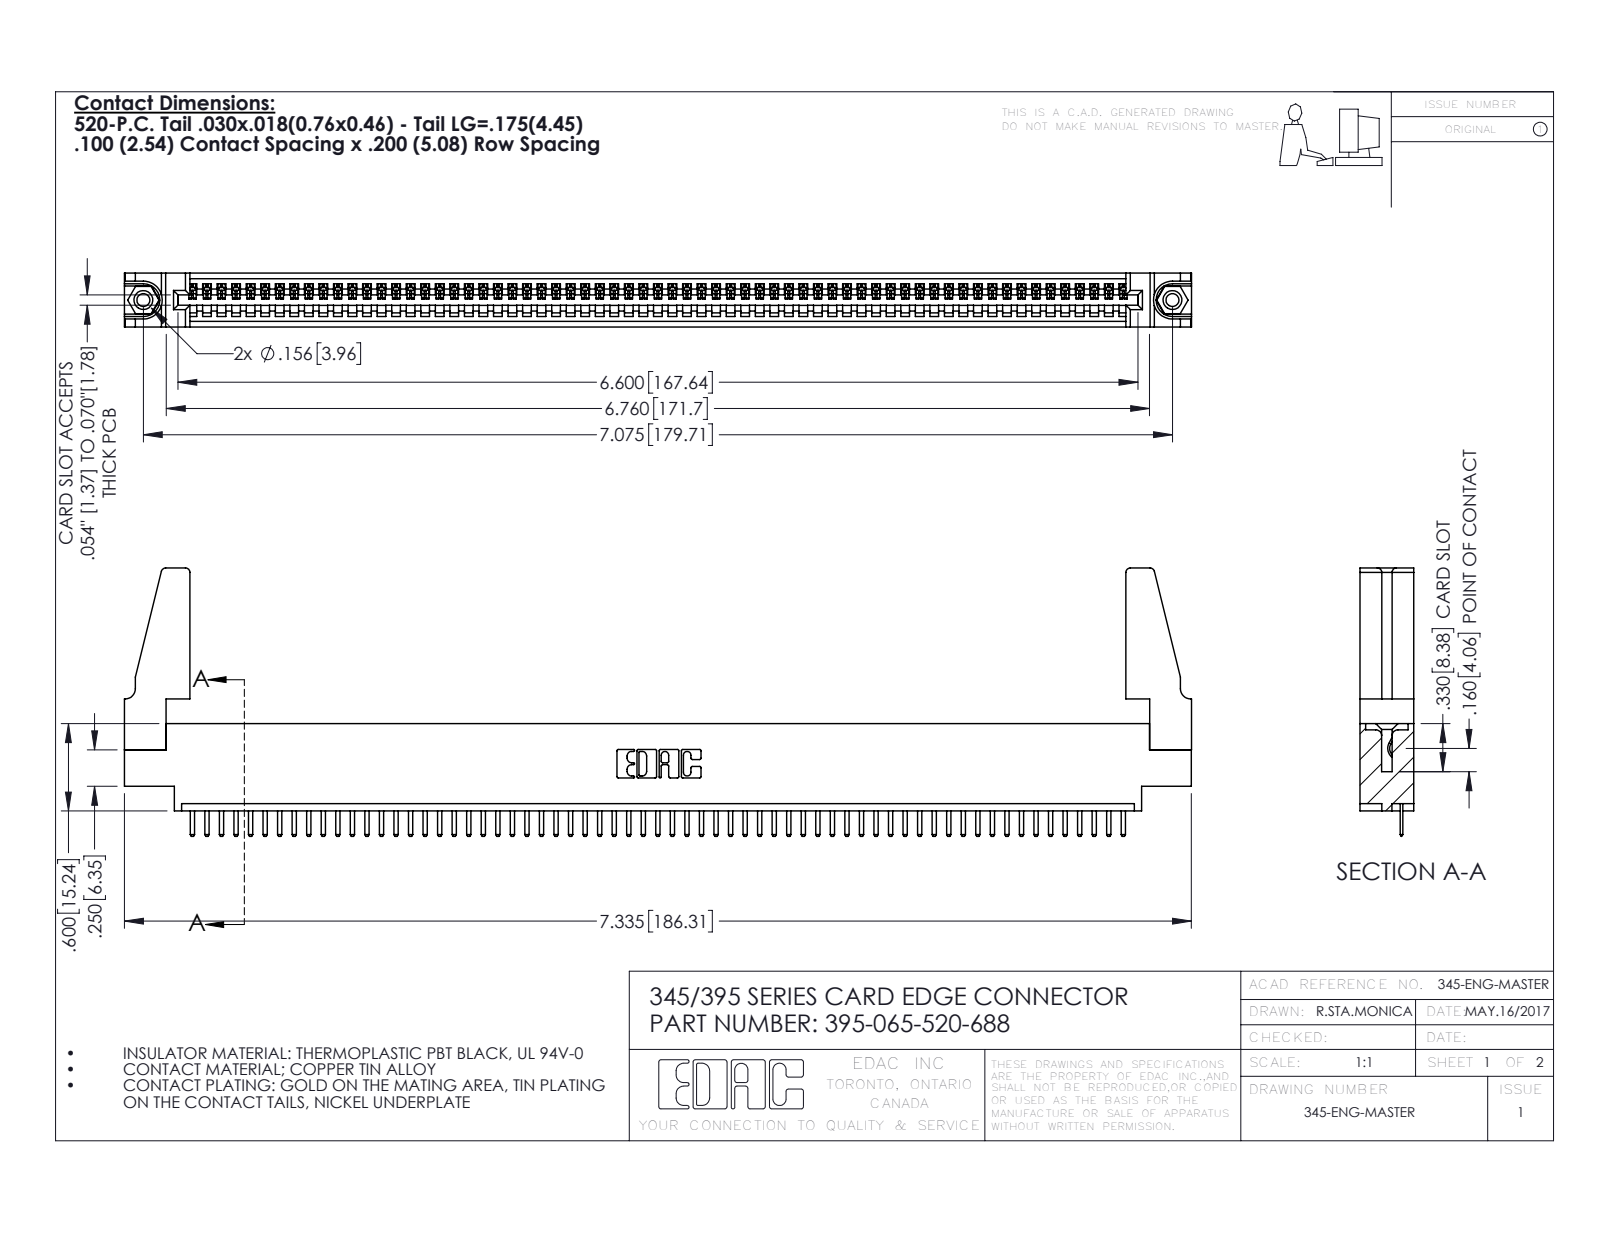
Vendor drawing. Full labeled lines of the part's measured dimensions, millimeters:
Part name (STEP PRODUCT): 345-220-078_345-220-088; 395-065-520-688; 345-250-001_345-250-001-102; 345-292-001_345-293-120 (+1 more)
STEP written by: SolidWorks 2016 (CONFIG_CONTROL_DESIGN)
Units: millimetres
Bodies: 70 solids, 4284 faces (2886 planar, 1382 cylindrical, 16 other)
Overall size (bounding box): 186.3 × 46.9 × 9.4
Volume: 20 840 mm³ · Surface area: 26 330 mm²
Round holes (diameter × count): ⌀2.3 ×2, ⌀3.2 ×2, ⌀4 ×2, ⌀1.6 ×1
Round bosses / shafts (diameter × count): ⌀3.9 ×2
Partial cylindrical surfaces — rounded edges, fillets, slot ends (radius × count): R0.3 ×132, R0.2 ×130, R0.3 ×22, R0.8 ×8, R0.2 ×6, R0.8 ×6, R0.7 ×3, R0.8 ×2
Main face-to-face distances: 1.8, 9.4, 7.6, 5.1, 2.5, 6.9, 0.6, 5.7, 1.8, 4.4
Hole centre spacings: 6.9, 173.7, 179.7
